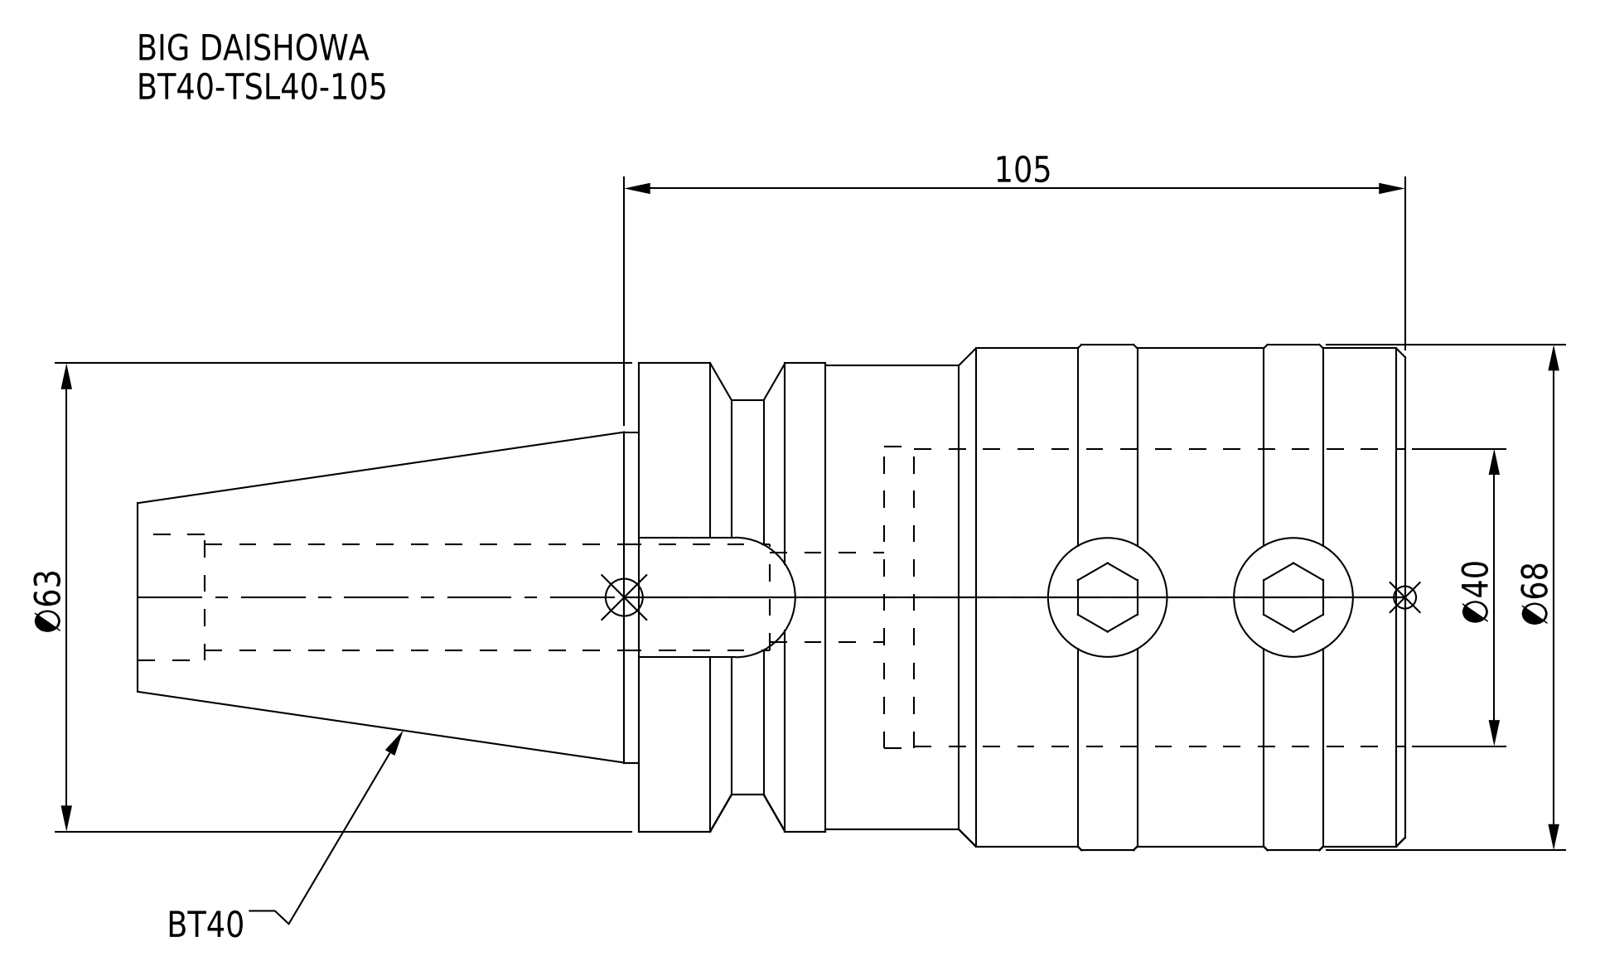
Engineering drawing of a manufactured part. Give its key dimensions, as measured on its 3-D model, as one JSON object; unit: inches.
{"part_name": "BT40-TSL40-105", "step_written_by": "CREO PARAMETRIC BY PTC INC, 2016380 (AUTOMOTIVE_DESIGN)", "units": "inches", "bodies": {"solids": 1, "faces": 66, "planar": 14, "cylindrical": 34, "other": 18}, "overall_size": [6.709, 2.677, 2.677], "volume_in3": 18.18, "surface_area_in2": 75.5, "round_holes": [[0.472, 1], [0.559, 1], [0.669, 1], [1.575, 1], [1.598, 1]], "round_bosses_or_shafts": [[2.677, 1], [2.638, 1], [2.48, 1], [2.457, 1], [2.087, 1], [1.75, 1]], "partial_cylinders_radius": [[0.317, 1]], "face_to_face_distances": [4.055, 2.756, 1.299, 1.772, 6.709, 3.953, 2.654, 0.634, 6.354, 3.598]}
